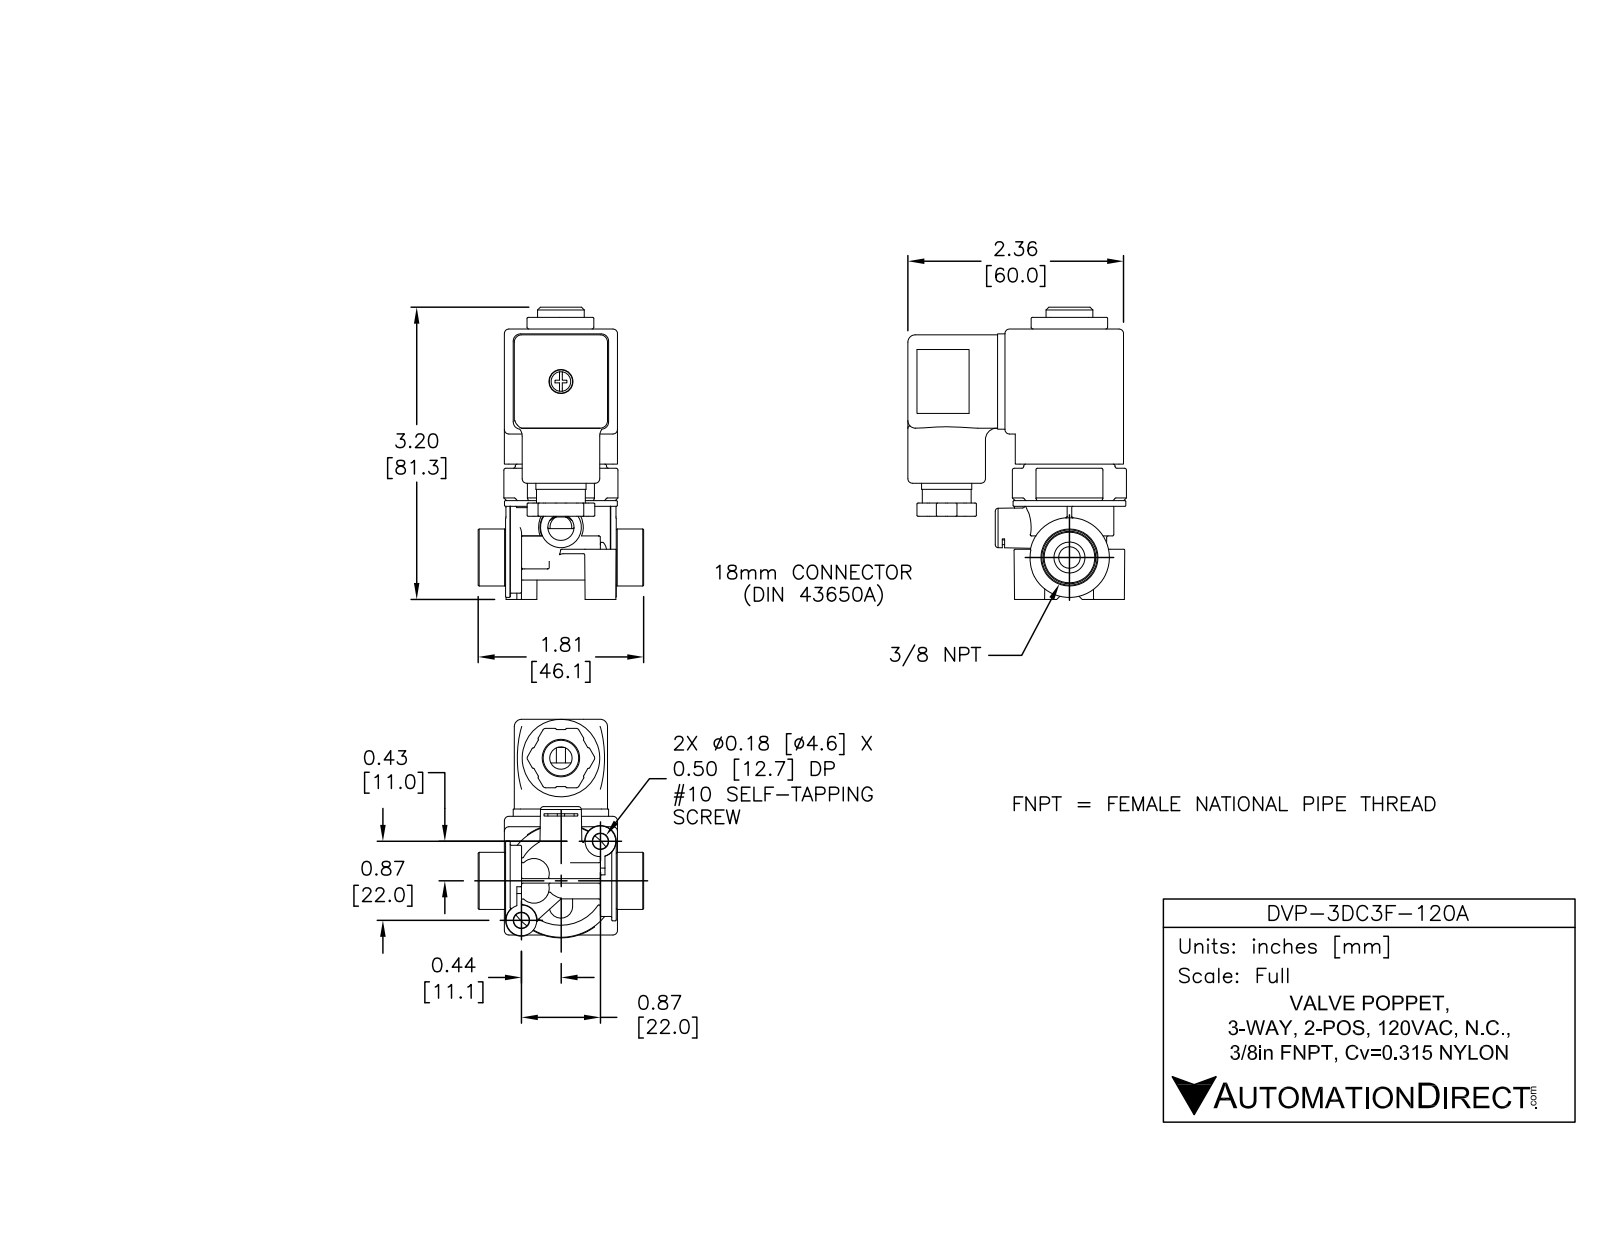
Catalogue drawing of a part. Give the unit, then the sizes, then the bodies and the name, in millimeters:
Units: millimetres
Overall size (bounding box): 81.4 × 60.8 × 46.1
Round holes (diameter × count): ⌀1.5 ×2, ⌀6 ×2, ⌀2.4 ×1, ⌀2.4 ×1, ⌀2.6 ×1, ⌀3 ×1, ⌀3.5 ×1, ⌀5.2 ×1, ⌀6.2 ×1, ⌀6.4 ×1, ⌀6.7 ×1, ⌀7.3 ×1
Round bosses / shafts (diameter × count): ⌀7.4 ×2, ⌀31.4 ×1, ⌀25.4 ×1, ⌀24.7 ×1, ⌀22.6 ×1, ⌀22.2 ×1, ⌀22.2 ×1, ⌀21.6 ×1
Partial cylindrical surfaces — rounded edges, fillets, slot ends (radius × count): R0.3 ×74, R0.4 ×34, R1.3 ×21, R0.5 ×12, R2 ×12, R0.7 ×6, R0.8 ×6, R1 ×4
Main face-to-face distances: 27.5, 31.5, 1.2, 4, 2, 23.5, 36, 37.6, 2.8, 28.7
Hole centre spacings: 7.1, 7.2, 27, 34.1, 34.2, 40.9, 41.3, 55.5
Volume: 64 240 mm³ · Surface area: 35 660 mm²
Bodies: 6 solids, 1790 faces (806 planar, 344 cylindrical, 640 other)
Part name (STEP PRODUCT): DVP-3DC3F-120A
STEP written by: SolidWorks 2015 (AUTOMOTIVE_DESIGN)
